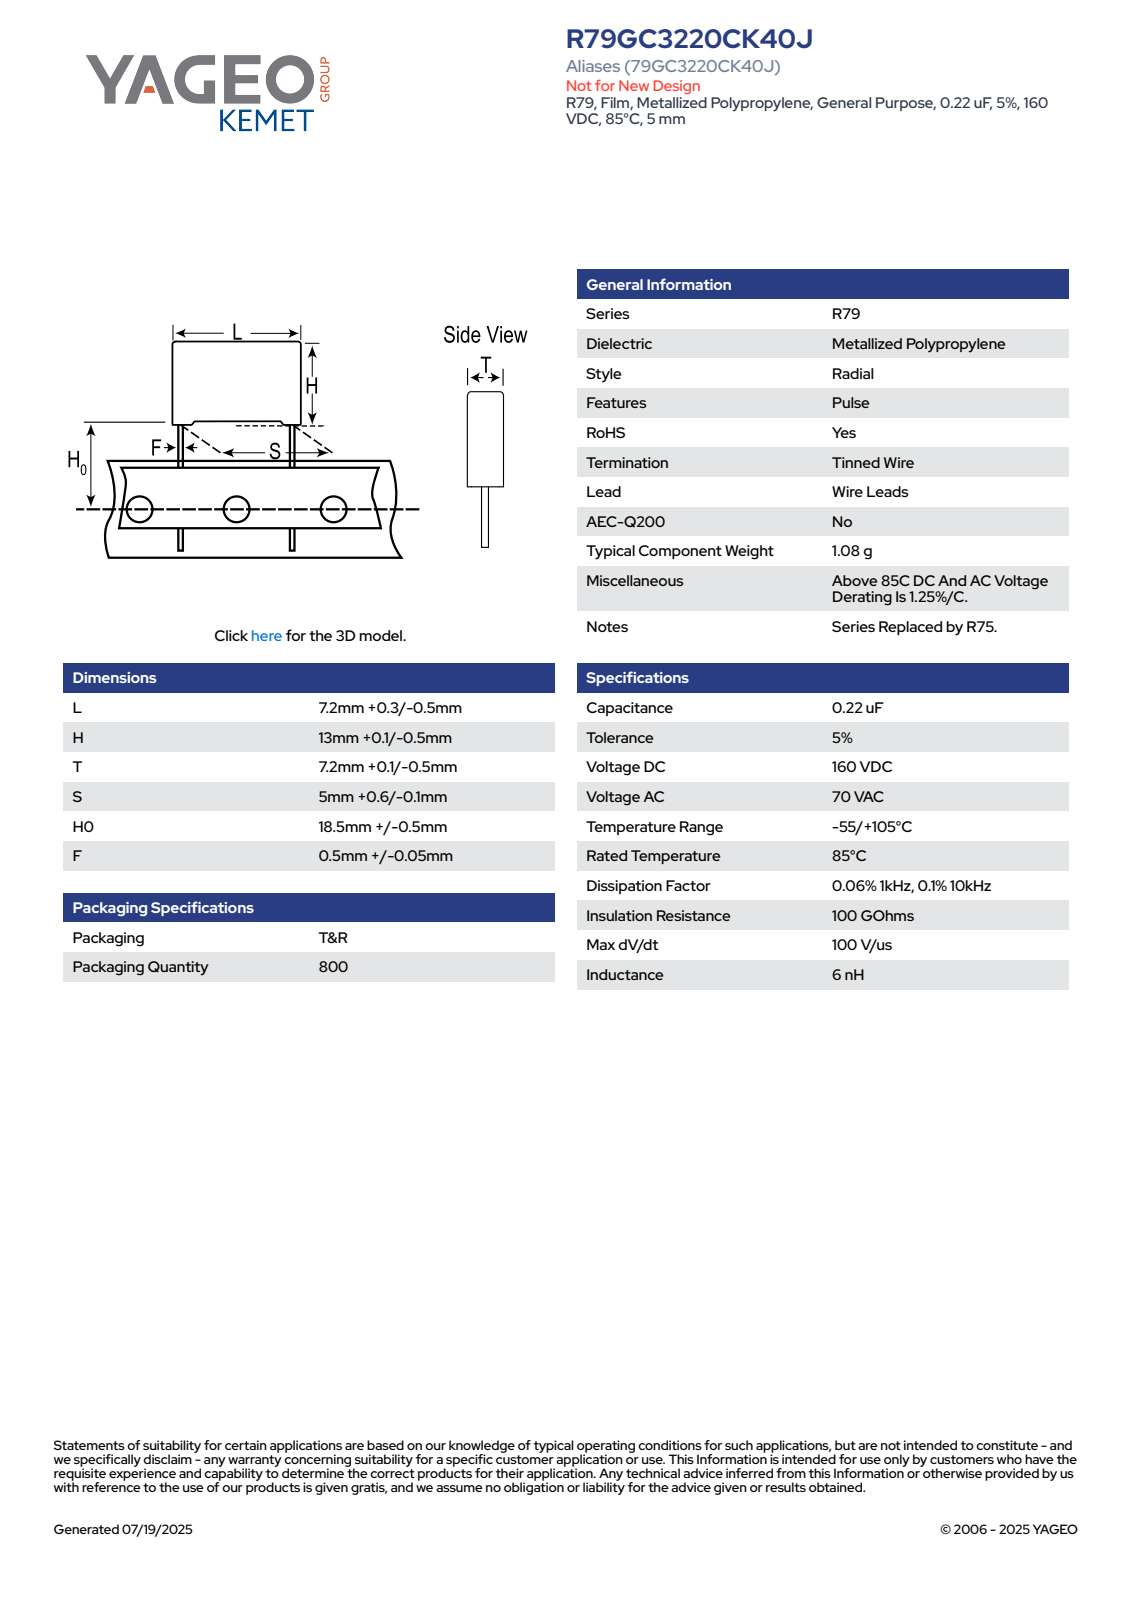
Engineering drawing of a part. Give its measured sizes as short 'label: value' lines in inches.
name: CFR_RB2_7.2X13X7.2_L7.5H13.1T7.3S5H019F0.55
written by: SolidWorks 2020 (AUTOMOTIVE_DESIGN)
unit: in
bodies: 4 solids, 85 faces (77 planar, 8 cylindrical, 0 other)
size: 1.264 × 0.295 × 0.287
volume: 0.042 in³; area: 0.901 in²
bosses: 2× ⌀0.022
rounds: 4× R0.02
face distances: 0.287, 0.295, 0.486, 0.285, 0.278, 0.03, 0.516, 0.276, 0.268, 0.018
